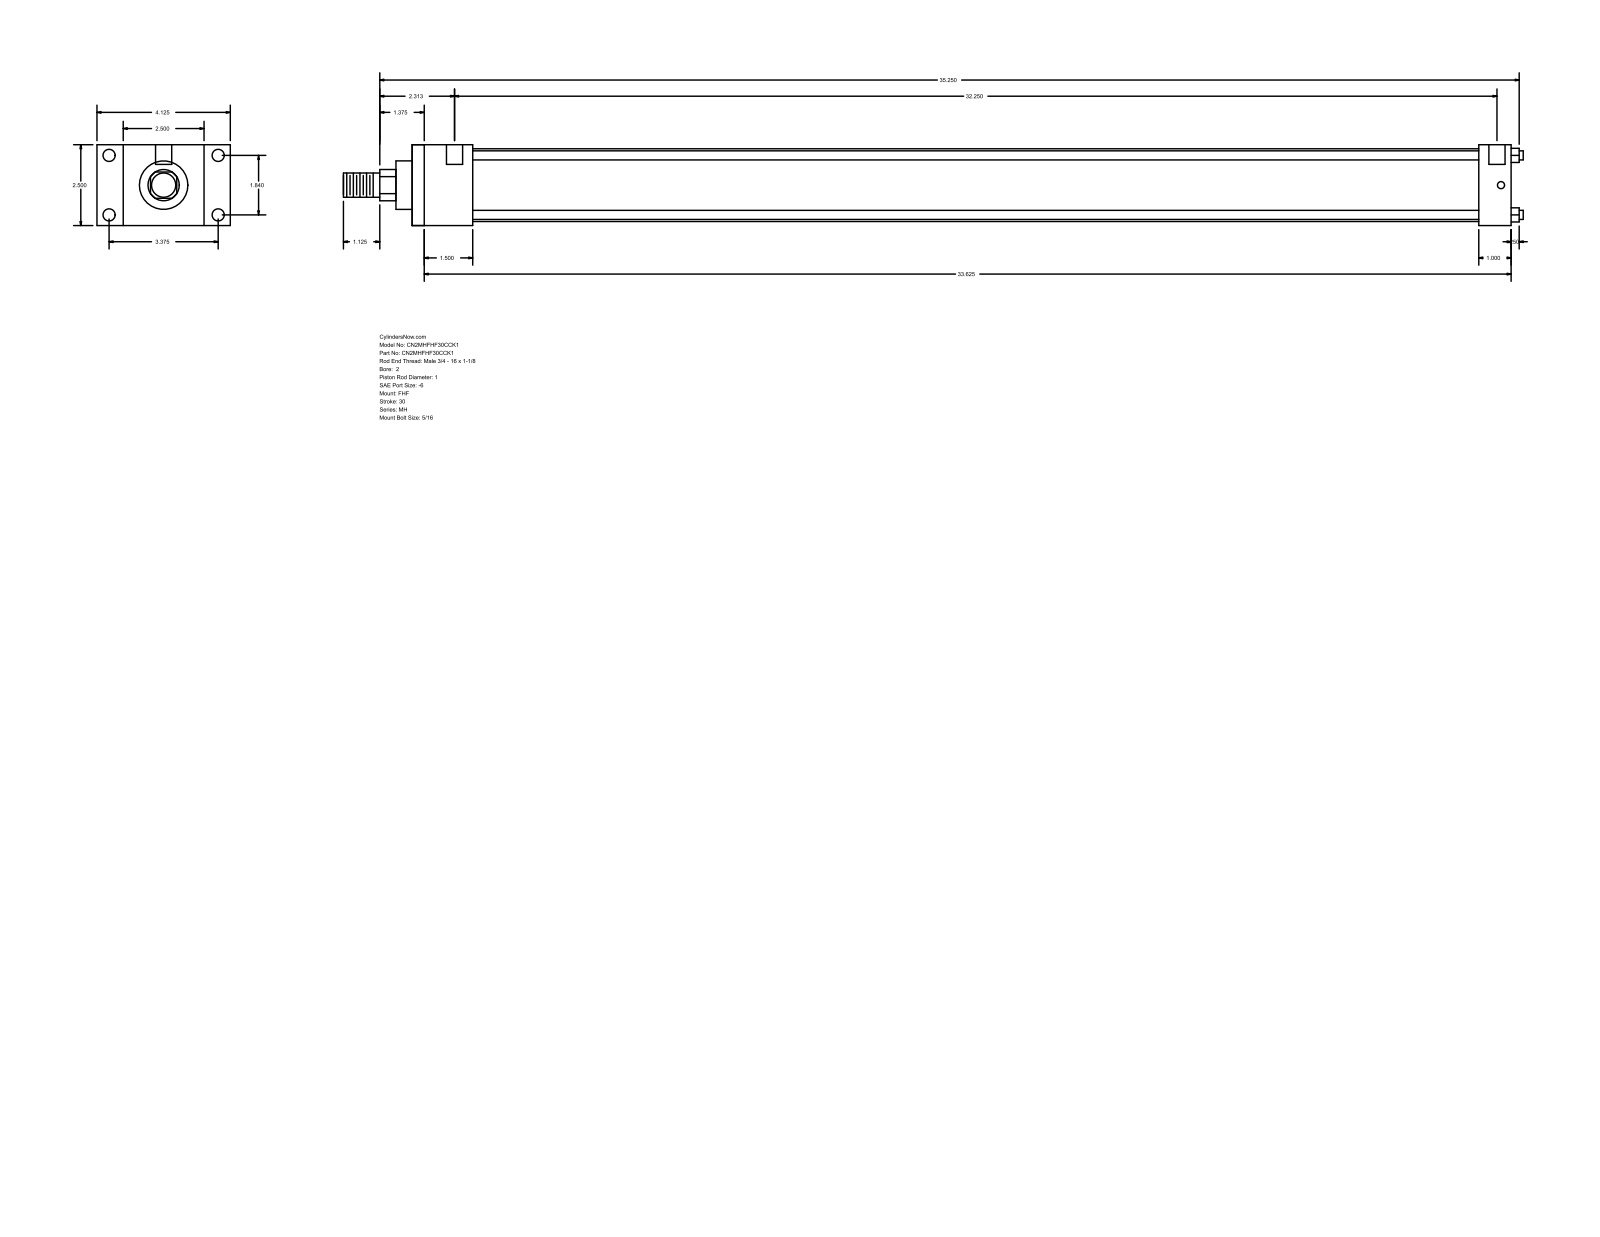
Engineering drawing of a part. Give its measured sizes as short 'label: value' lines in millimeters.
name: MH_FHF__0200_1
written by: GSSL Pune (CONFIG_CONTROL_DESIGN)
unit: mm
bodies: 0 solids, 88 faces (60 planar, 28 cylindrical, 0 other)
size: 927.1 × 104.78 × 63.5
holes: 4× ⌀5.56, 4× ⌀9.53, 2× ⌀12.7
bosses: 4× ⌀7.14, 1× ⌀57.15, 1× ⌀38.1, 1× ⌀25.4, 1× ⌀19.05
rounds: 1× R12.29
face distances: 63.5, 863.6, 47.63, 815.97, 20.64, 84.14, 104.78, 25.4, 838.2, 790.57
hole spacings: 46.74, 85.72, 97.63, 827.08, 3.17, 4.76, 819.15, 822.32
